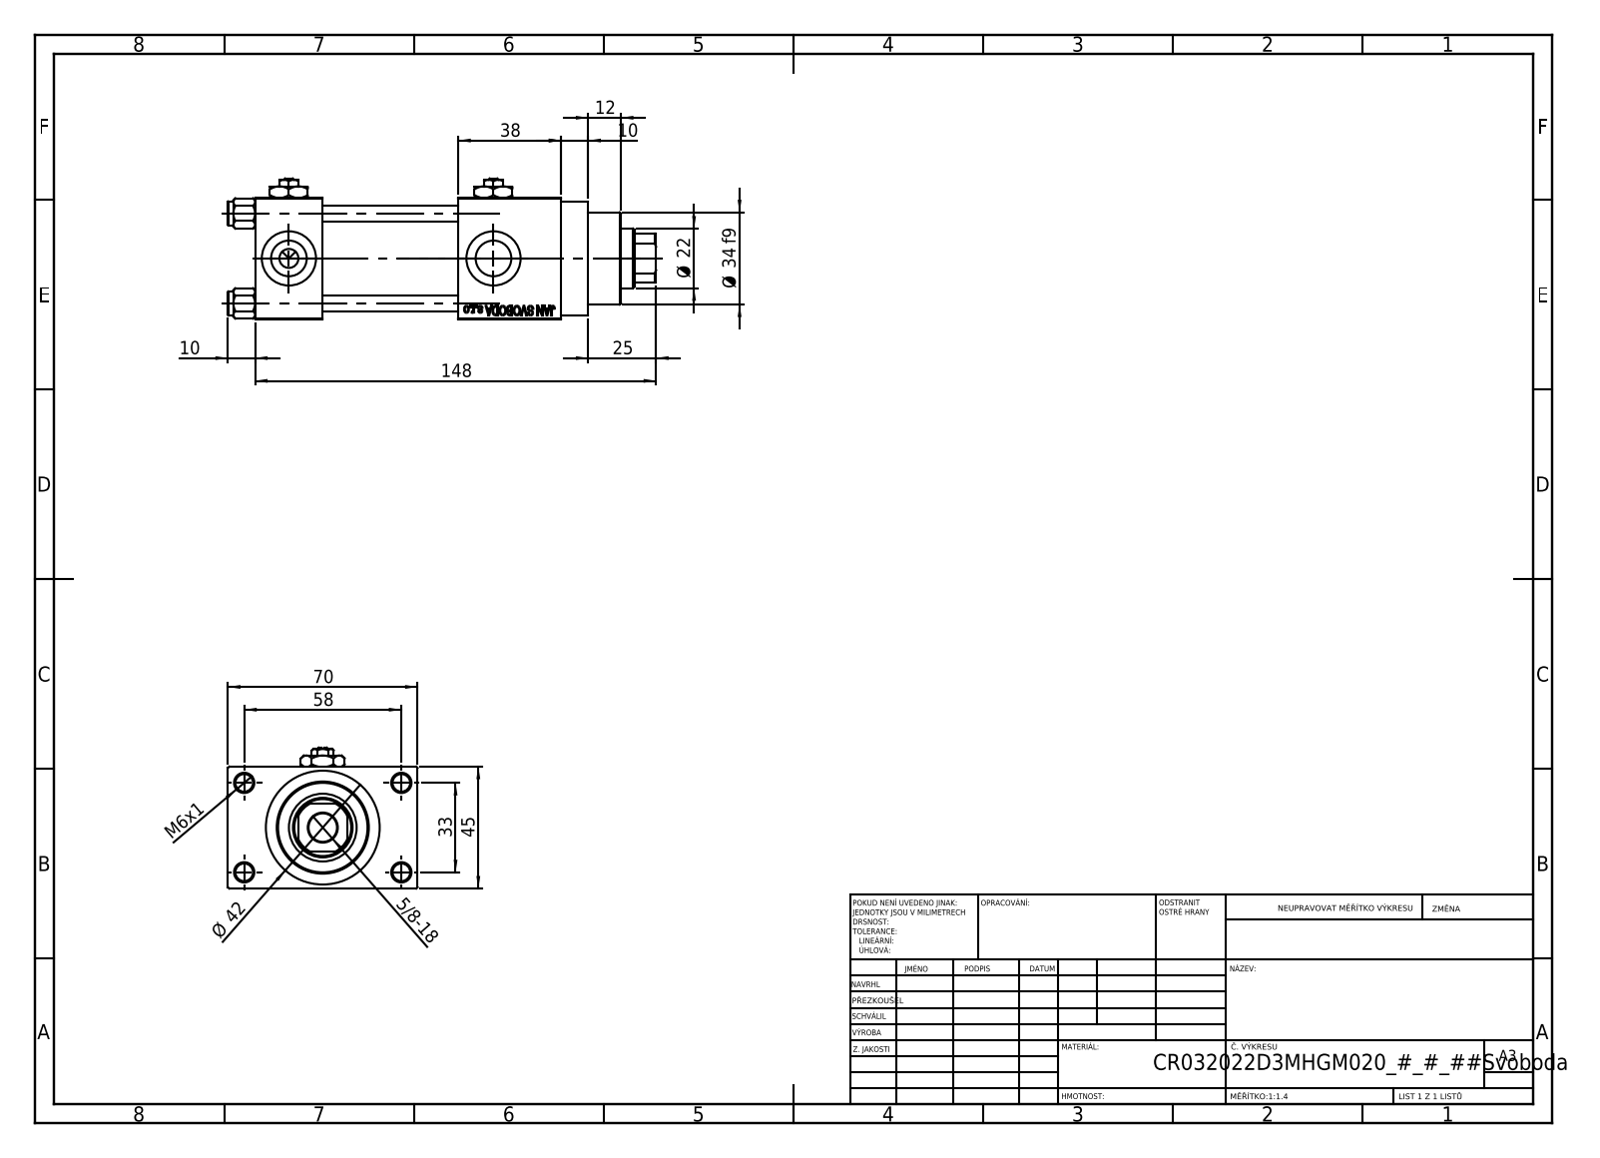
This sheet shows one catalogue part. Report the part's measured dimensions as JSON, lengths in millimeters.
{"part_name": "NUT_M5_D; V215CR_D_TYCINKA; Zatka_pro_OIL_PORT; V215CR_D_Body (+2 more)", "step_written_by": "SolidWorks 2019 (CONFIG_CONTROL_DESIGN)", "units": "millimeters", "bodies": {"solids": 13, "faces": 1201, "planar": 542, "cylindrical": 99, "other": 560}, "overall_size": [158, 70, 52], "volume_mm3": 241745, "surface_area_mm2": 81712, "round_holes": [[6, 4], [6.5, 4], [13.16, 4], [20, 4], [7, 3], [10.5, 1], [22, 1], [24, 1], [25, 1], [32, 1], [33, 1]], "round_bosses_or_shafts": [[9, 4], [42, 1], [38, 1], [34, 1]], "partial_cylinders_radius": [[10.5, 1]], "face_to_face_distances": [45, 25, 50, 12.5, 75, 57.5, 88, 38, 113, 70], "hole_center_spacings": [12.4, 23.48, 33.2, 33.37, 35.35, 45.6, 56.35, 33]}
